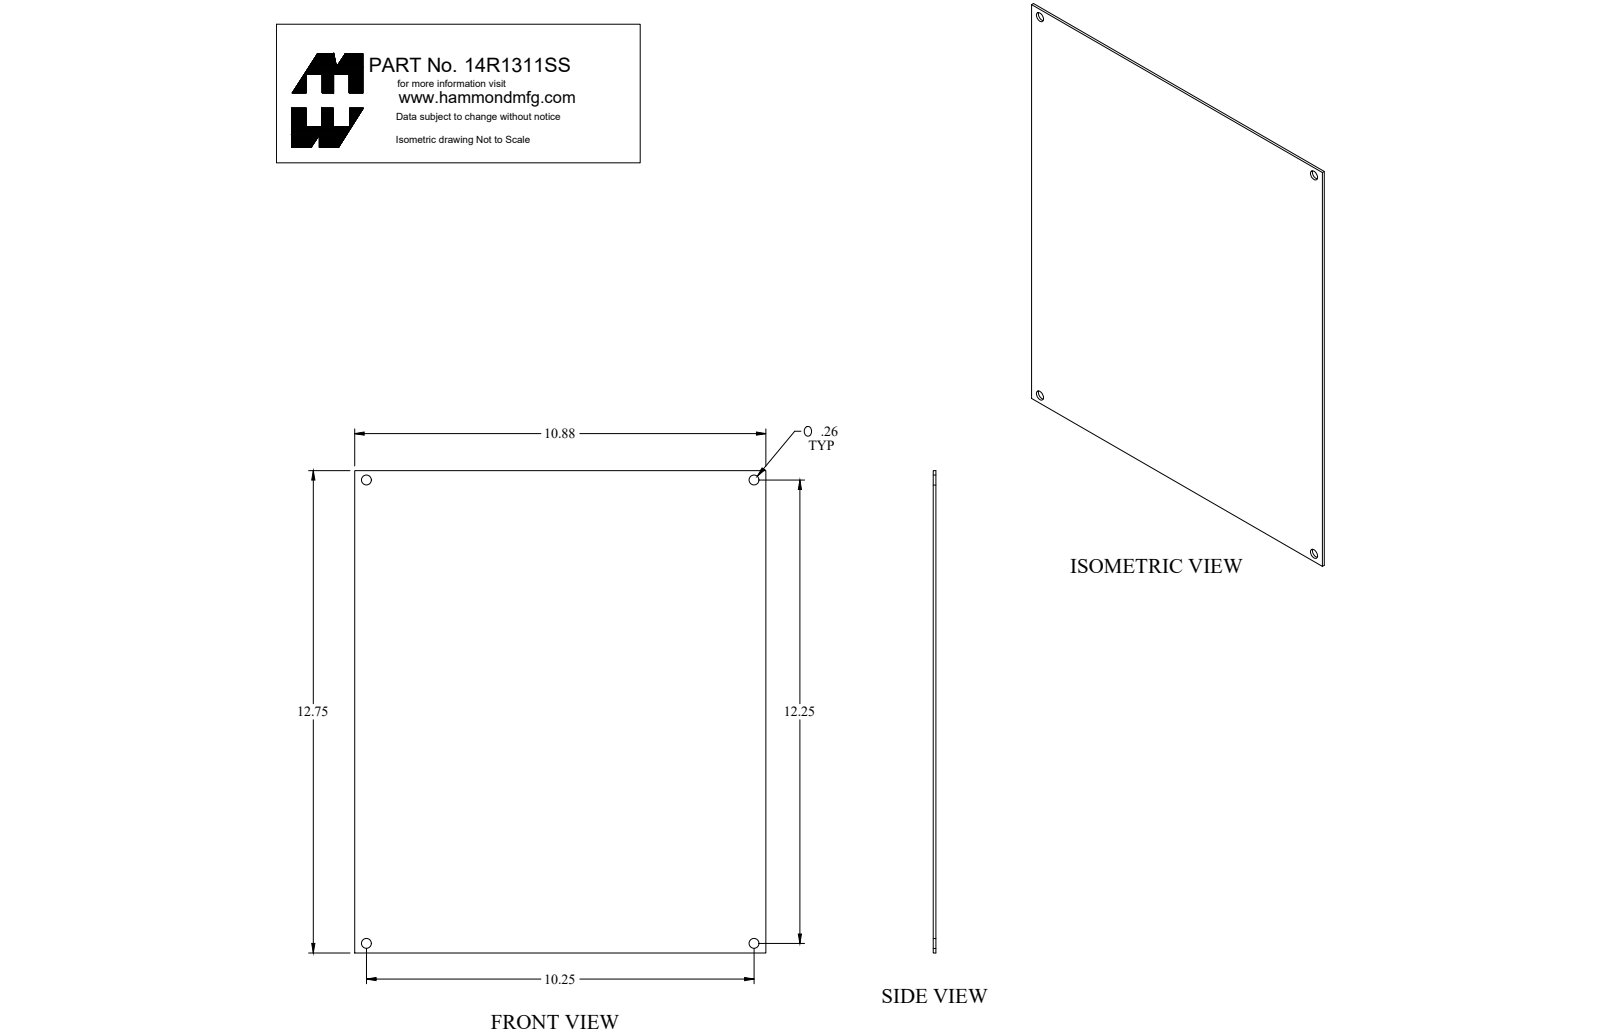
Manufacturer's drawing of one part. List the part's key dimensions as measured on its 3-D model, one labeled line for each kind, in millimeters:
Part name (STEP PRODUCT): 14R1311SS
STEP written by: SolidWorks 2018 (AUTOMOTIVE_DESIGN)
Units: millimetres
Bodies: 1 solid, 10 faces (6 planar, 4 cylindrical, 0 other)
Overall size (bounding box): 323.9 × 276.2 × 1.8
Volume: 163 300 mm³ · Surface area: 181 000 mm²
Round holes (diameter × count): ⌀6.7 ×4
Main face-to-face distances: 1.8, 276.2, 323.9
Hole centre spacings: 260.4, 311.2, 405.7
